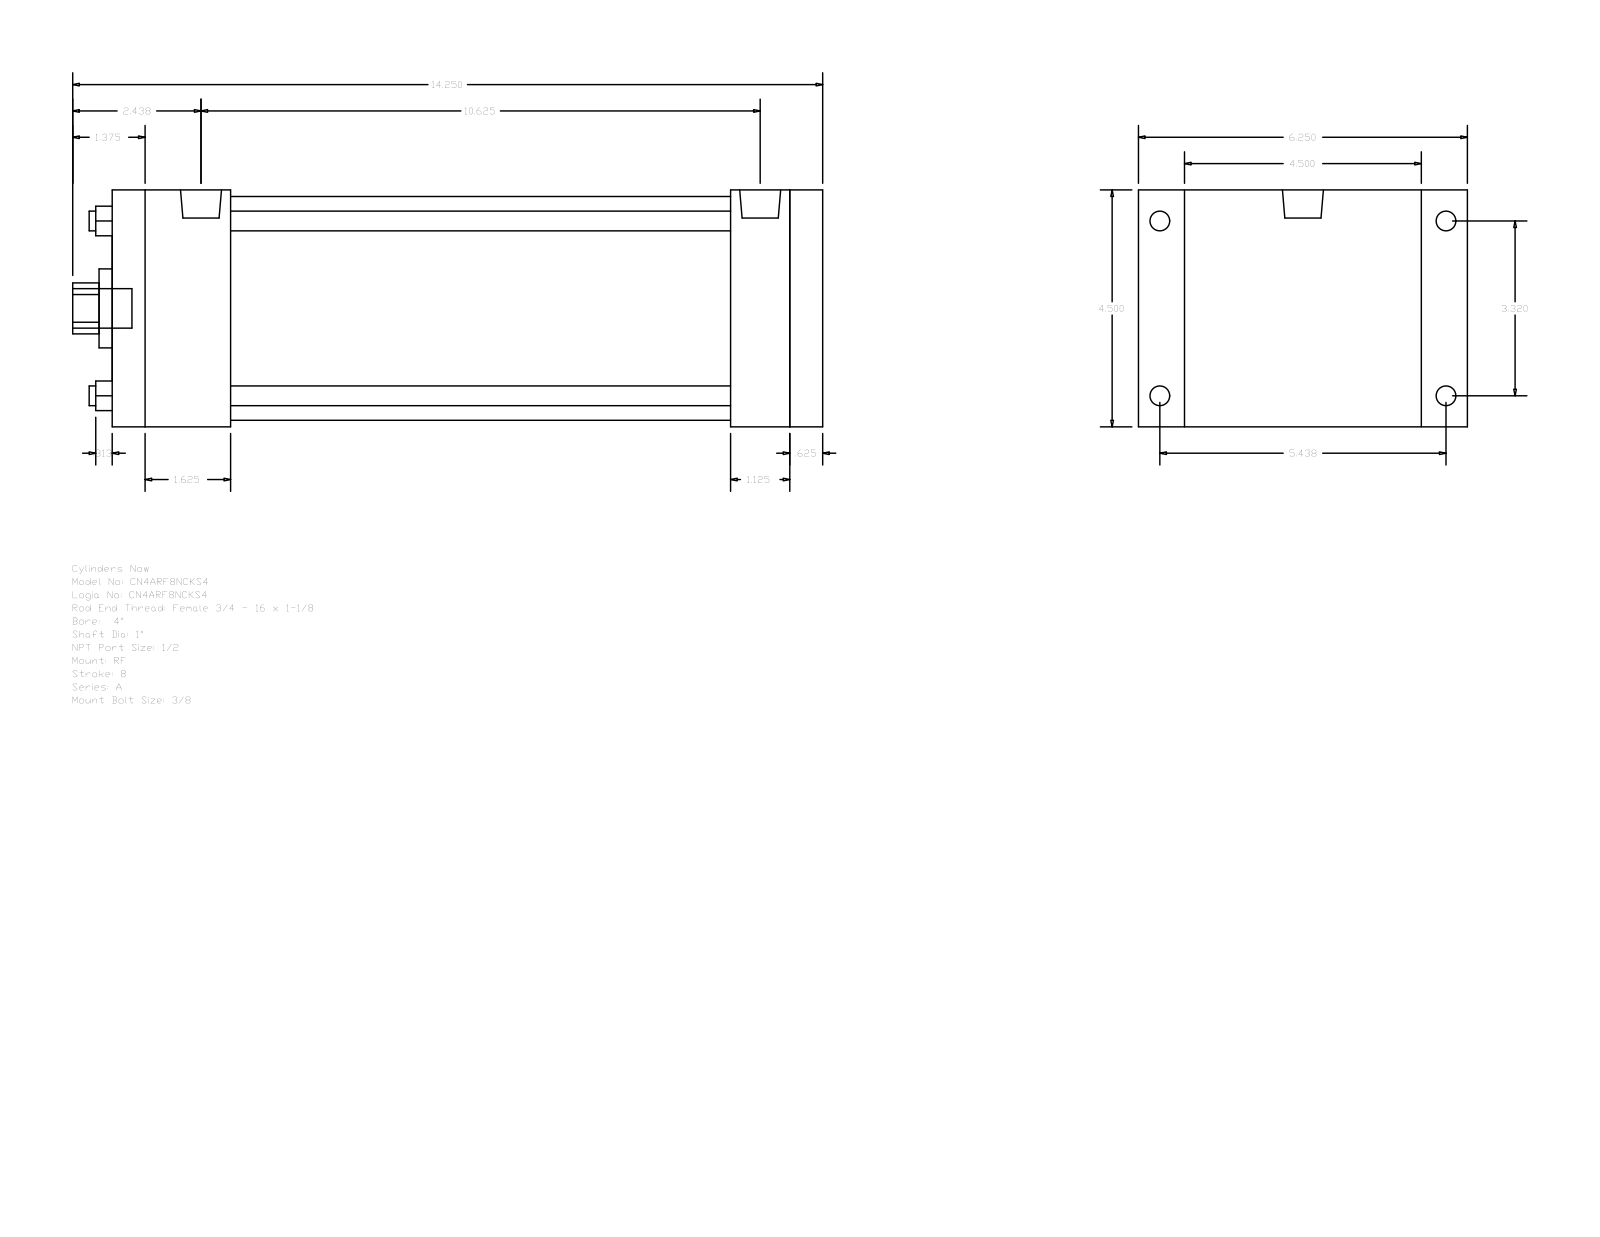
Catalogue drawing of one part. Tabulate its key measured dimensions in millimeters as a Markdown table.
| quantity | value |
| --- | --- |
| part name | A_RF__0400_1 |
| STEP written by | GSSL Pune (CONFIG_CONTROL_DESIGN) |
| units | millimeters |
| bodies | 0 solids, 92 faces (64 planar, 28 cylindrical, 0 other) |
| overall size | 361.95 × 158.75 × 114.3 |
| round holes (diameter × count) | 9.53 × 4, 25.4 × 1, 38.1 × 1, 107.95 × 1 |
| round bosses / shafts (diameter × count) | 9.53 × 4, 8.73 × 4, 19.77 × 2, 19.05 × 1 |
| partial cylindrical surfaces (radius × count) | 12.29 × 1 |
| main face-to-face distances | 114.3, 342.9, 327.02, 15.88, 28.57, 22.23, 136.53, 298.45, 44.45, 57.15 |
| hole center spacings | 59.62, 84.32, 119.25 |
